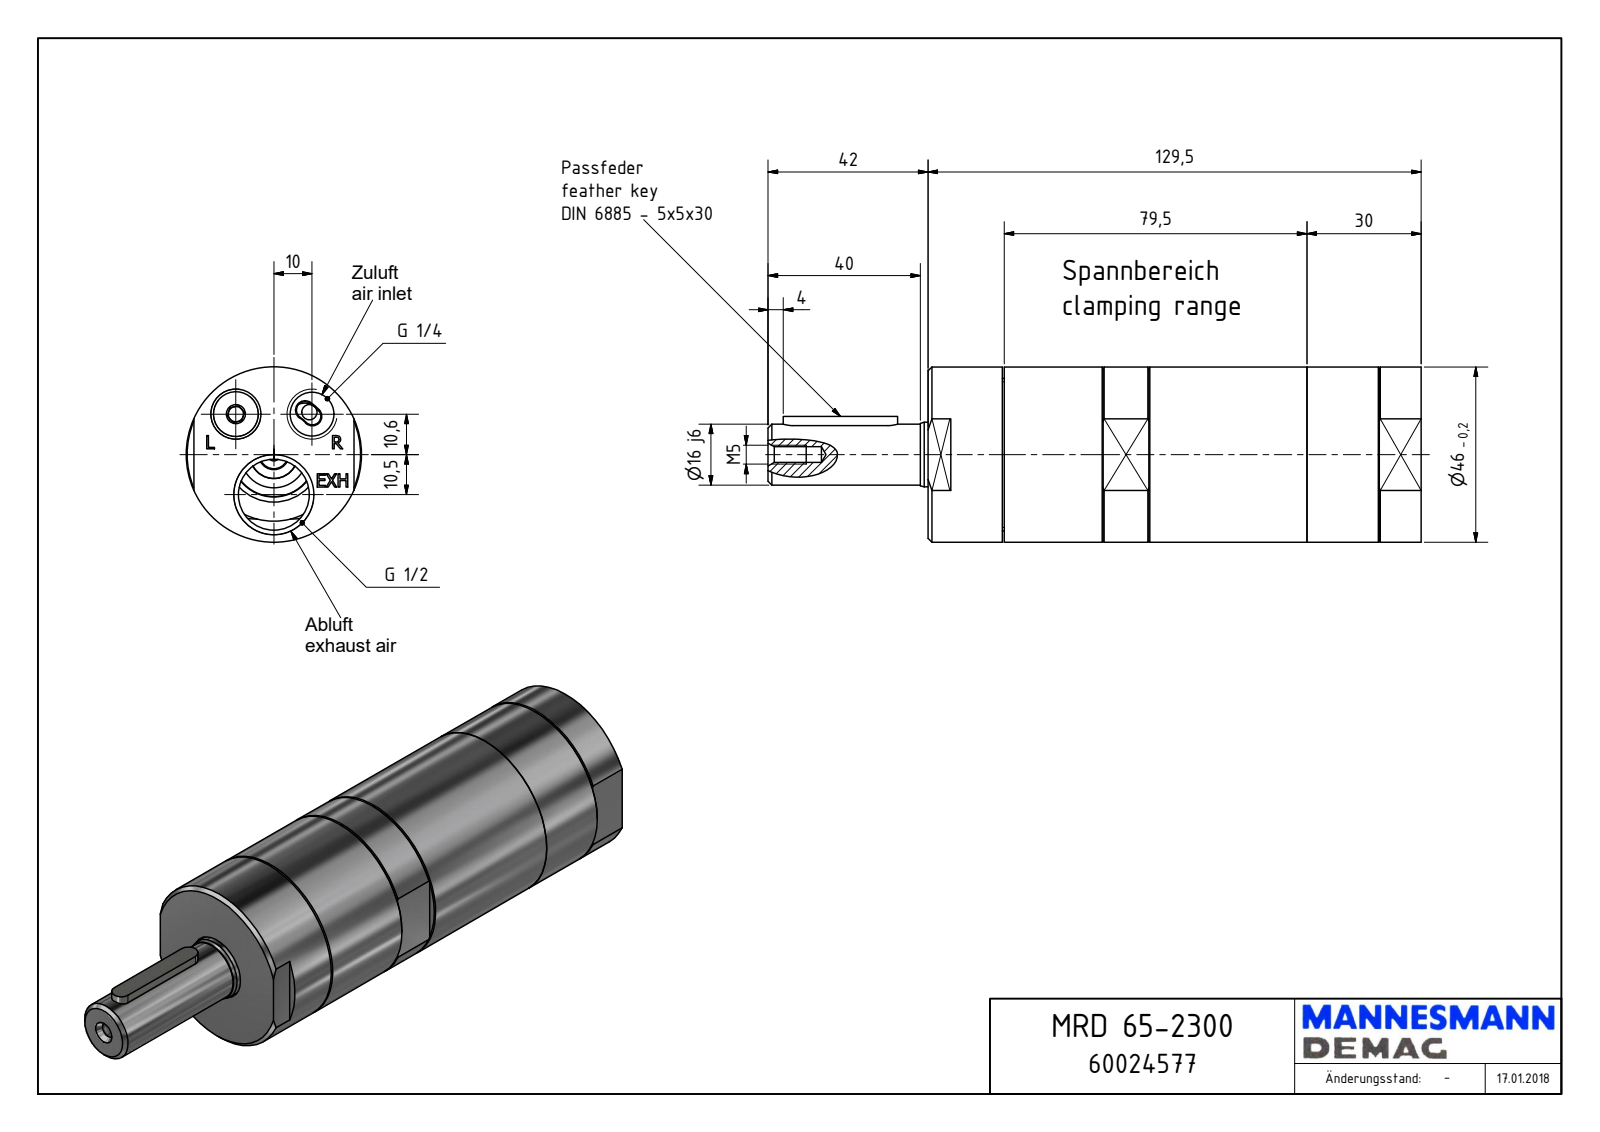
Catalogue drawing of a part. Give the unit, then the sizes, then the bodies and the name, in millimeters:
Units: millimetres
Overall size (bounding box): 171.5 × 46 × 46
Round holes (diameter × count): ⌀4 ×1, ⌀4.13 ×1, ⌀11.45 ×1, ⌀17.5 ×1, ⌀18.63 ×1
Round bosses / shafts (diameter × count): ⌀46 ×1, ⌀40 ×1, ⌀16.95 ×1, ⌀16 ×1
Partial cylindrical surfaces — rounded edges, fillets, slot ends (radius × count): R2.5 ×2, R5 ×2, R5.72 ×1, R17.23 ×1, R19 ×1
Main face-to-face distances: 129.5, 42, 20, 109.5, 19.5, 0.5, 110, 121.77, 102.27, 101.77
Hole centre spacings: 14.57, 23.35, 10.5, 20
Volume: 218 167 mm³ · Surface area: 27 372 mm²
Bodies: 1 solid, 159 faces (105 planar, 26 cylindrical, 28 other)
Part name (STEP PRODUCT): MRD 65-2300_60024577
STEP written by: Autodesk Inventor 2018 (AUTOMOTIVE_DESIGN)
